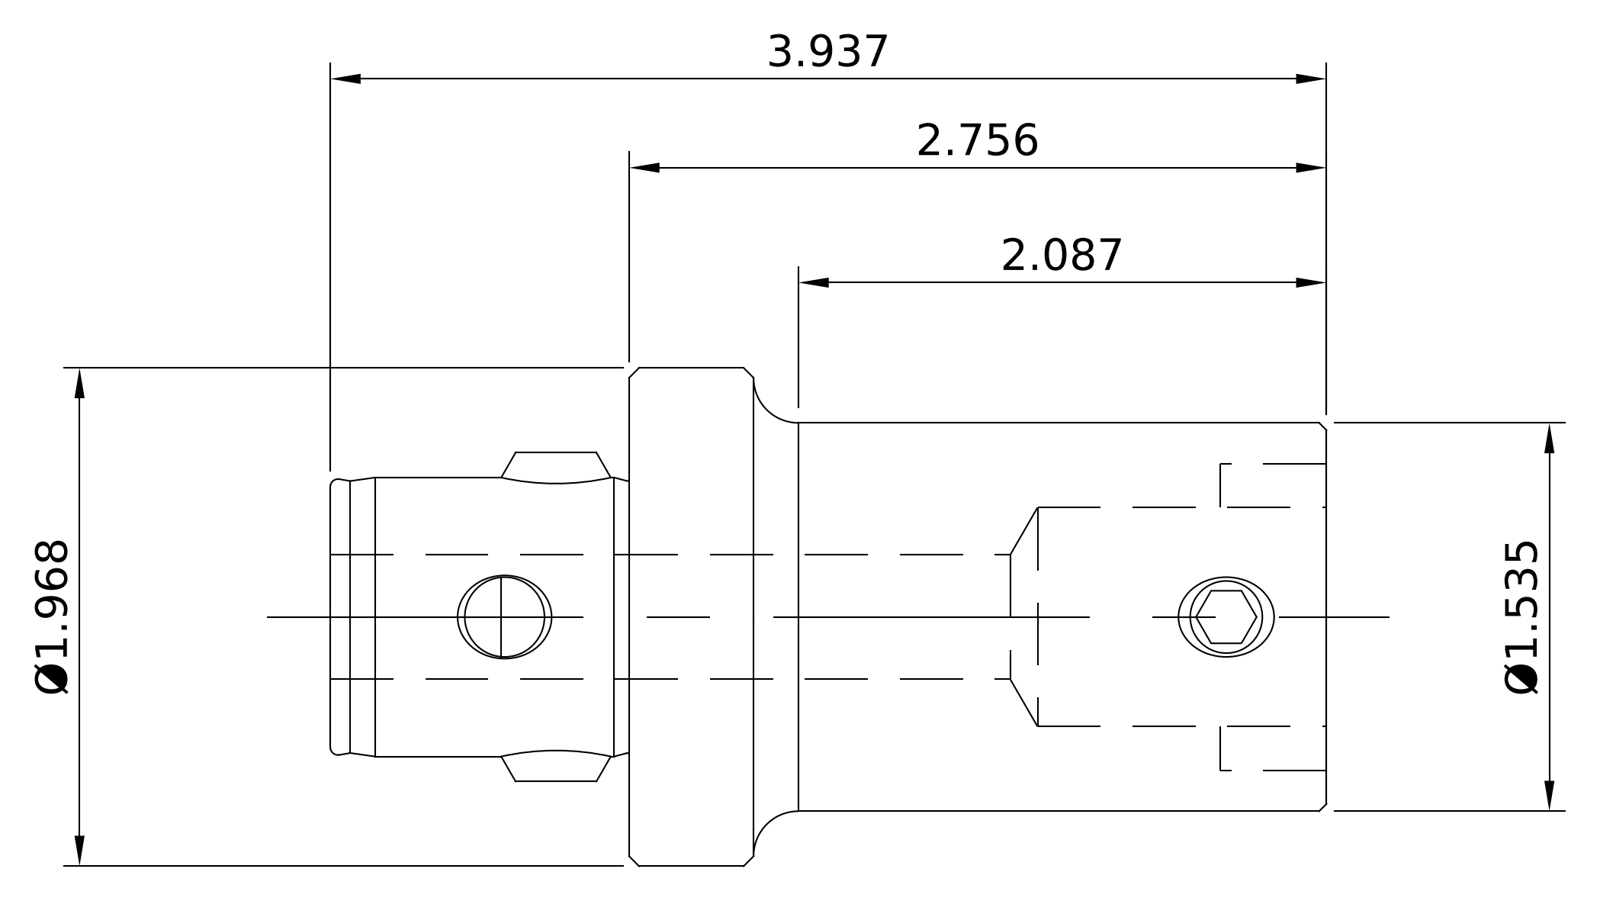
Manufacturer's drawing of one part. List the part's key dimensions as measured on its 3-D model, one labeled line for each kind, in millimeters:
Part name (STEP PRODUCT): 11.332.540; 10.332.54X_10.332.540; 10.332.540_11.332.540; 10.690.43X_10.690.434 (+2 more)
STEP written by: SolidWorks 2014 (AUTOMOTIVE_DESIGN)
Units: millimetres
Bodies: 4 solids, 151 faces (42 planar, 51 cylindrical, 58 other)
Overall size (bounding box): 100 × 50 × 50
Volume: 89 435 mm³ · Surface area: 22 445 mm²
Round holes (diameter × count): ⌀4.5 ×1, ⌀6.8 ×1, ⌀8 ×1, ⌀8.2 ×1, ⌀11 ×1, ⌀12 ×1, ⌀12.5 ×1, ⌀14.5 ×1, ⌀16.5 ×1, ⌀22 ×1, ⌀22.5 ×1
Round bosses / shafts (diameter × count): ⌀50 ×1, ⌀39 ×1, ⌀38.6 ×1, ⌀28 ×1, ⌀10.9 ×1, ⌀8.8 ×1, ⌀8 ×1, ⌀6.9 ×1
Partial cylindrical surfaces — rounded edges, fillets, slot ends (radius × count): R3.5 ×2, R14 ×1
Main face-to-face distances: 70, 30, 100, 71, 41, 29, 18.9, 11, 4, 22
Hole centre spacings: 15, 72.45
